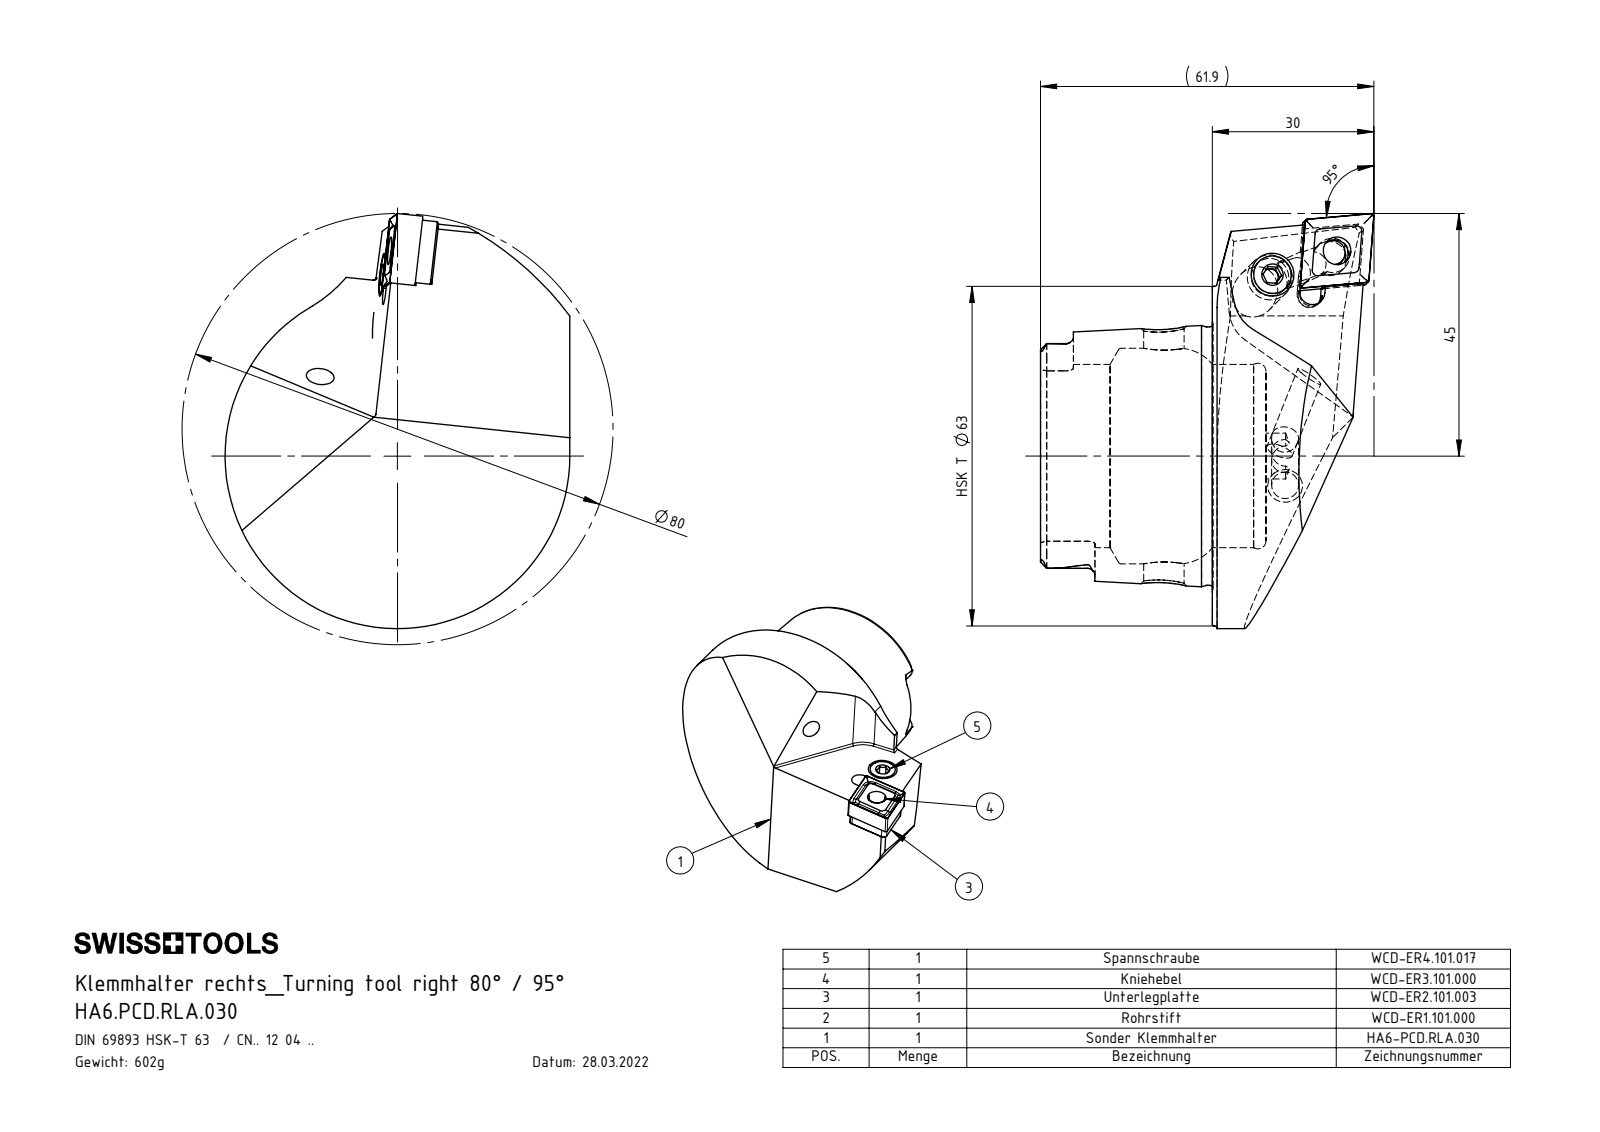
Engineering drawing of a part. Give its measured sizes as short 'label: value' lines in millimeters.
name: WCD-ER3.101.000_A; HA6.PCD.RLA.030; CNMG120404; WCD-ER4.101.017_A (+4 more)
written by: SolidWorks 2017 (AUTOMOTIVE_DESIGN)
unit: mm
bodies: 7 solids, 311 faces (107 planar, 88 cylindrical, 116 other)
size: 77 × 64 × 61.9
volume: 76 035 mm³; area: 24 763 mm²
holes: 2× ⌀5, 1× ⌀5.16, 1× ⌀6.4, 1× ⌀7, 1× ⌀7.5, 1× ⌀8.4, 1× ⌀8.5, 1× ⌀34, 1× ⌀40
bosses: 1× ⌀63, 1× ⌀47.94, 1× ⌀8, 1× ⌀7.9, 1× ⌀6.4, 1× ⌀6, 1× ⌀4.5, 1× ⌀3.55
rounds: 6× R1.4, 4× R0.4, 4× R1, 3× R0.5, 2× R2.5, 2× R2.82, 2× R2.88, 1× R2.1
face distances: 9.95, 31.9, 41.85, 4.46, 3.18, 7.64, 11.7, 1.01, 12.71, 12.21
hole spacings: 12.8, 12.86
